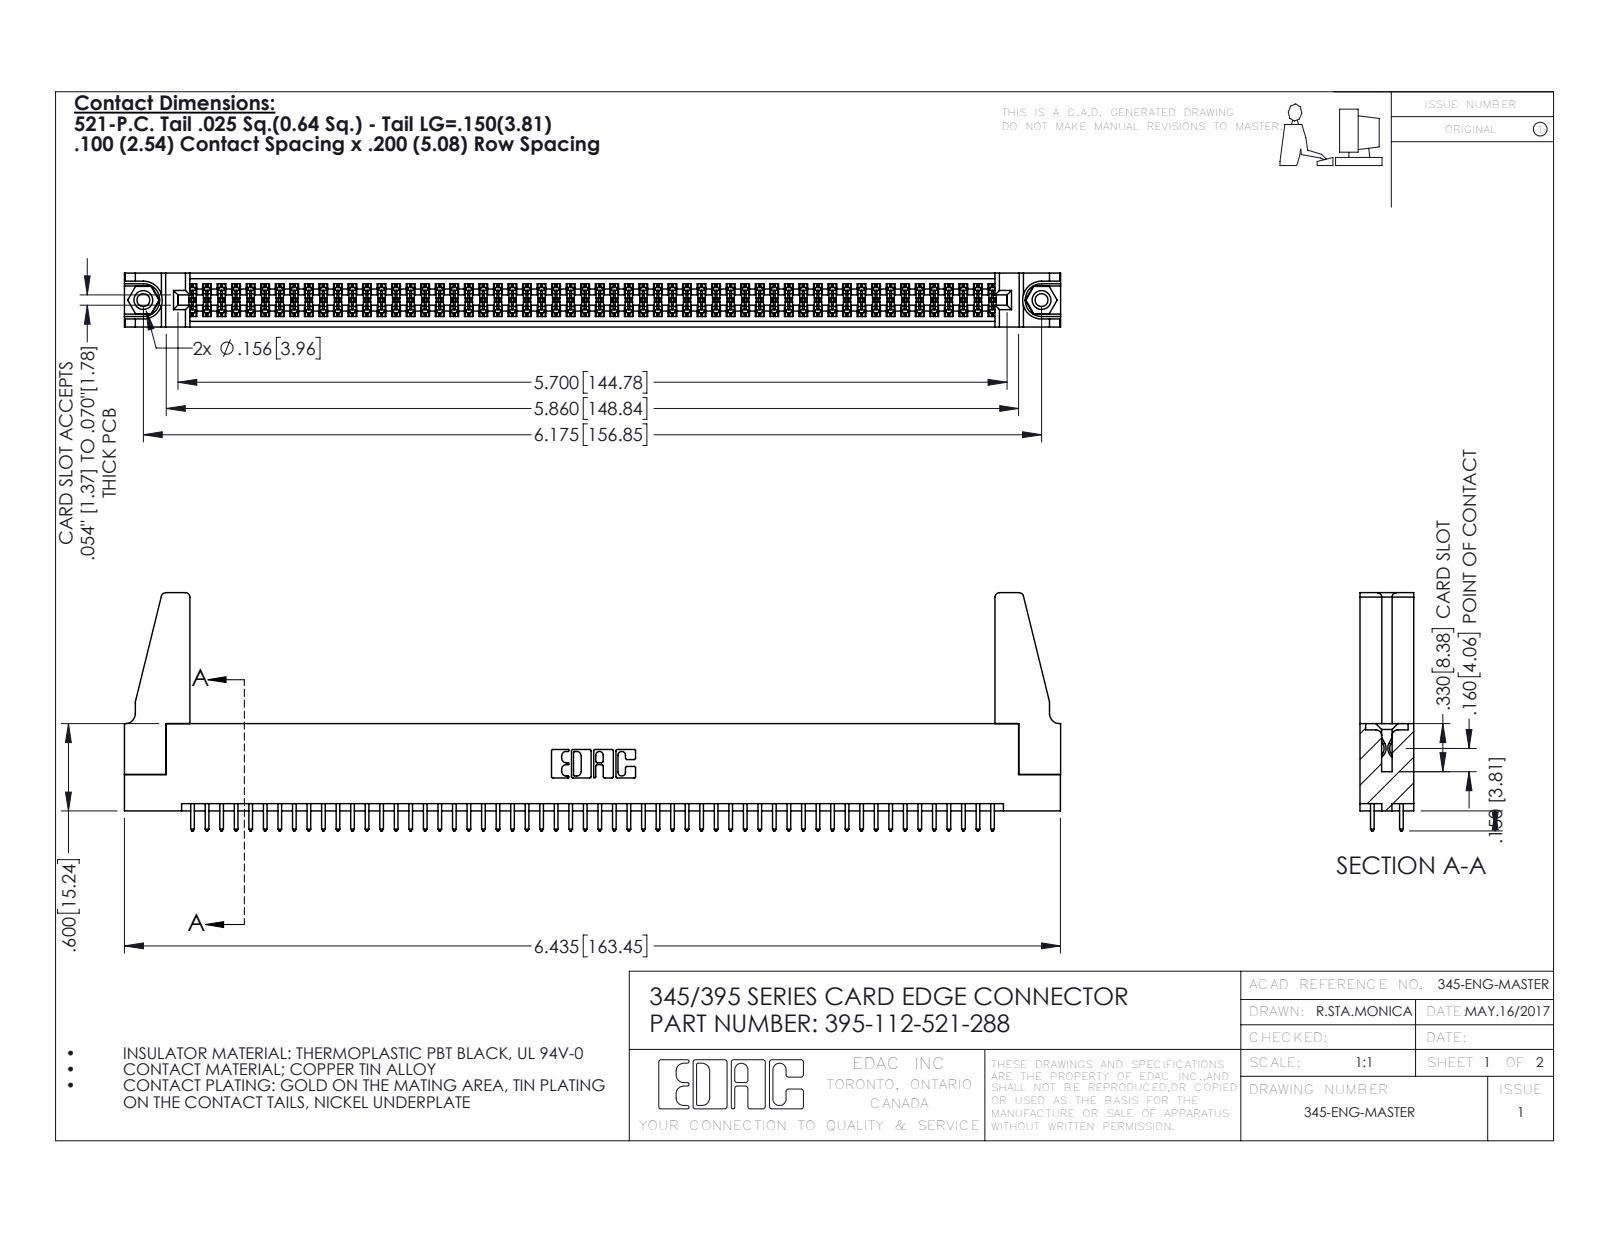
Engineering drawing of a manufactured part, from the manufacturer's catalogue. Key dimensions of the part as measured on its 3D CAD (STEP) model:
Part name (STEP PRODUCT): 345-220-078_345-220-088; 345-292-001_345-293-121; 395-112-521-288; 345 Part_Flush Mounting Lugs - 0.156 Dia-TH (+1 more)
STEP written by: SolidWorks 2016 (CONFIG_CONTROL_DESIGN)
Units: inches
Bodies: 117 solids, 5850 faces (3848 planar, 1986 cylindrical, 16 other)
Overall size (bounding box): 6.436 × 1.637 × 0.37
Volume: 1.173 in³ · Surface area: 41.38 in²
Round holes (diameter × count): ⌀0.089 ×2, ⌀0.125 ×2, ⌀0.156 ×2, ⌀0.064 ×1
Round bosses / shafts (diameter × count): ⌀0.155 ×2
Partial cylindrical surfaces — rounded edges, fillets, slot ends (radius × count): R0.006 ×168, R0.01 ×112, R0.01 ×22, R0.03 ×8, R0.007 ×6, R0.031 ×6, R0.026 ×3, R0.014 ×2
Main face-to-face distances: 0.072, 0.298, 0.37, 0.2, 0.098, 0.272, 0.025, 0.225, 0.175, 0.149
Hole centre spacings: 0.27, 5.939, 6.175
